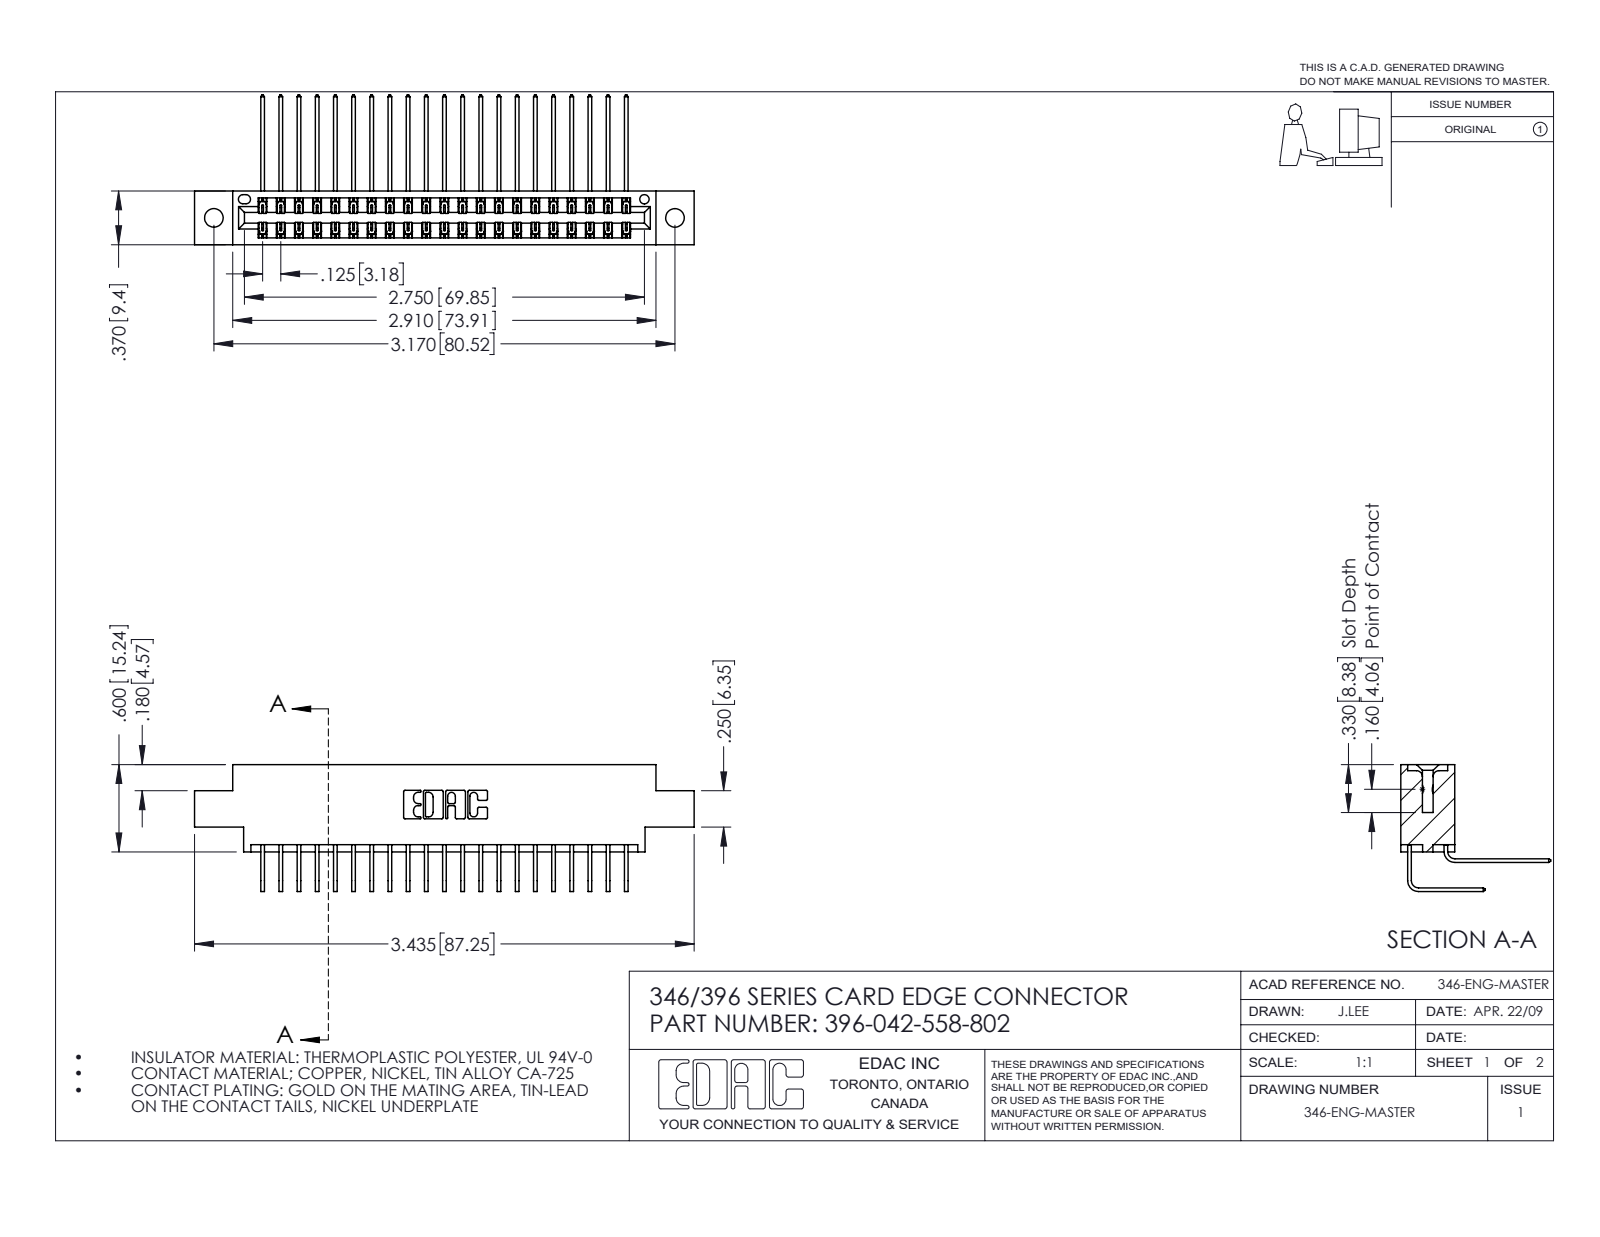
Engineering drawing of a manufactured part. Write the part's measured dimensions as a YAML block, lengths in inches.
part_name: "396-042-558-802; 345-292-001_558 559 Tail - 1; 345-292-001_558 Tail - 2; 346 Part_0.170 Offset - 0.128 Dia"
step_written_by: "SolidWorks 2016 (CONFIG_CONTROL_DESIGN)"
units: inches
bodies: {solids: 43, faces: 2394, planar: 1634, cylindrical: 760, other: 0}
overall_size: [3.435, 1.03, 0.873]
volume: 0.512
surface_area: 19.04
round_holes:
  - {diameter: 0.128, count: 2}
  - {diameter: 0.064, count: 1}
partial_cylinders:
  - {radius: 0.006, count: 63}
  - {radius: 0.01, count: 22}
  - {radius: 0.007, count: 6}
  - {radius: 0.031, count: 6}
  - {radius: 0.026, count: 3}
  - {radius: 0.014, count: 2}
  - {radius: 0.022, count: 2}
  - {radius: 0.024, count: 2}
face_to_face_distances: [0.322, 0.048, 0.37, 0.025, 0.25, 0.298, 0.072, 0.275, 0.148, 0.222]
hole_center_spacings: [0.246, 2.963, 3.17]
